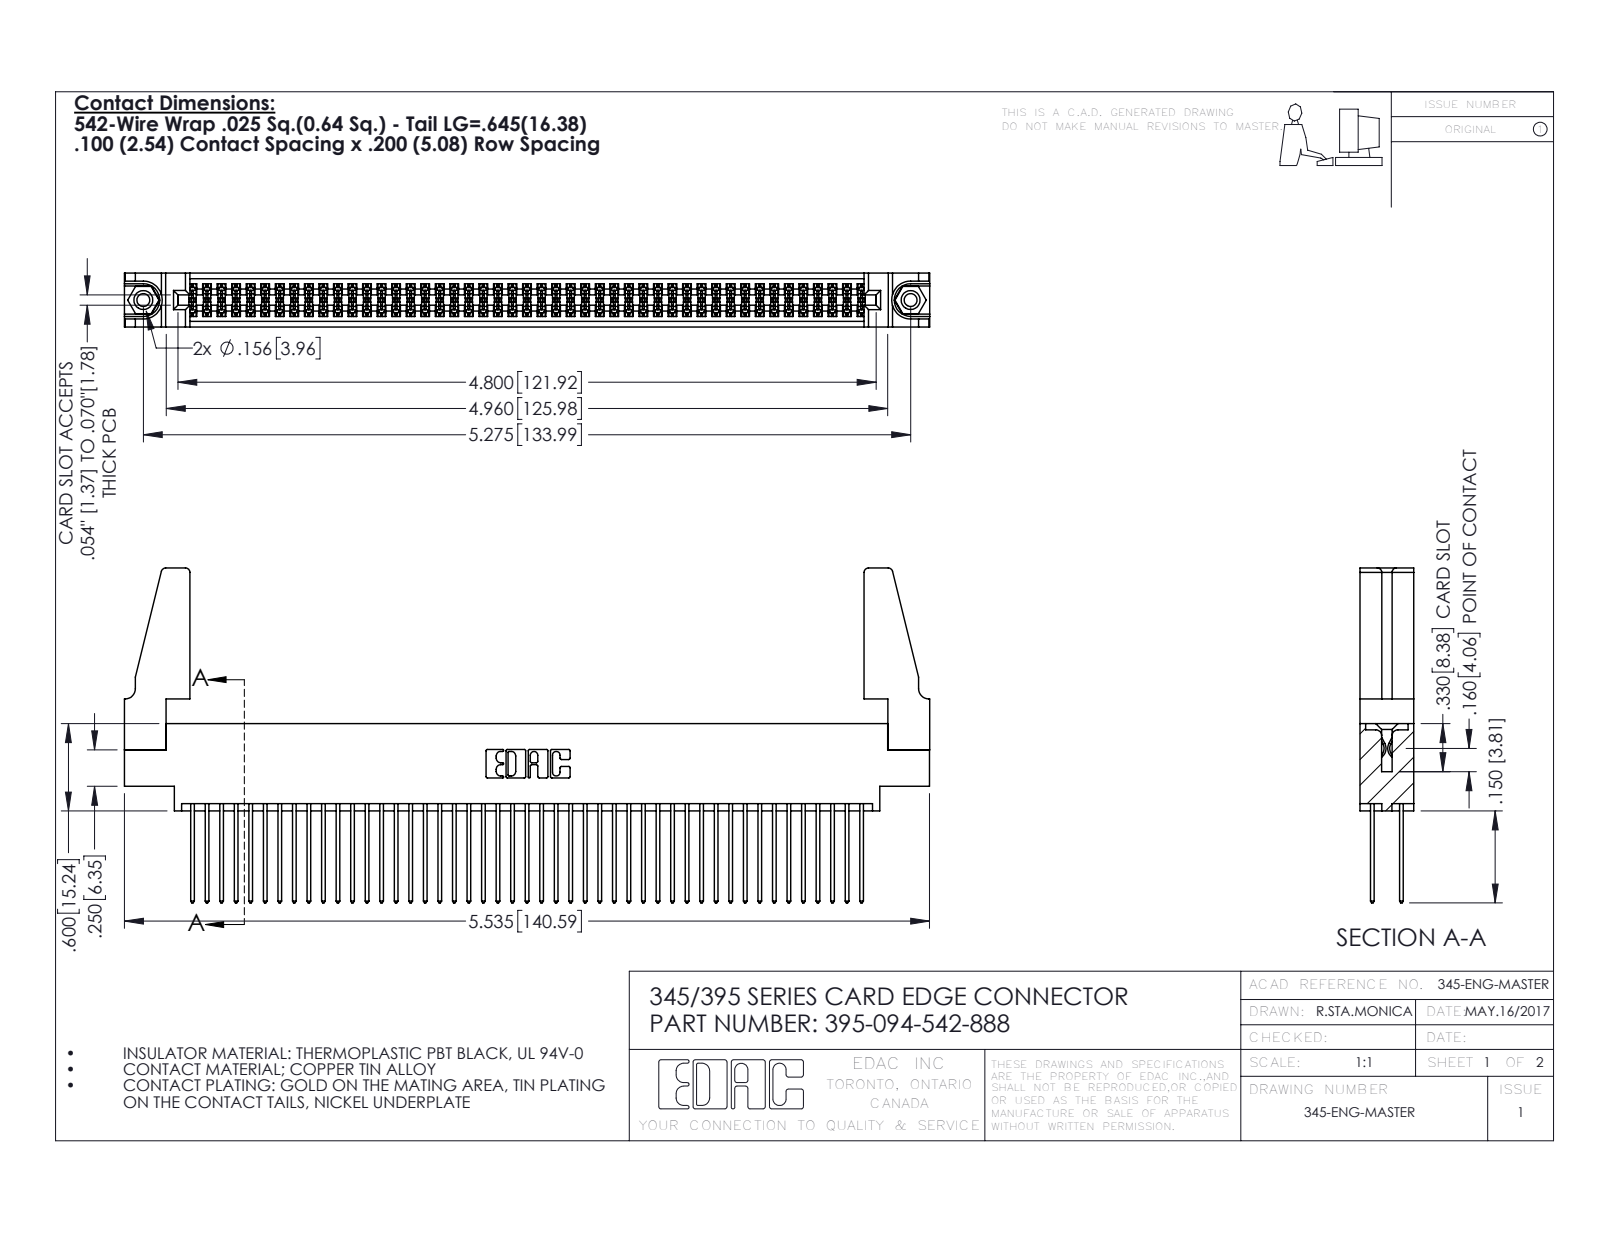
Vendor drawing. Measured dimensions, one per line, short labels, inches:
name: 345-250-001_345-250-001-102; 345 Part_0.170 Offset - 0.156 Dia-TH; 395-094-542-888; 345-220-078_345-220-088 (+1 more)
written by: SolidWorks 2016 (CONFIG_CONTROL_DESIGN)
unit: in
bodies: 99 solids, 4954 faces (3258 planar, 1680 cylindrical, 16 other)
size: 5.536 × 2.302 × 0.37
volume: 1.055 in³; area: 40.53 in²
holes: 2× ⌀0.089, 2× ⌀0.125, 2× ⌀0.156, 1× ⌀0.064
bosses: 2× ⌀0.155
rounds: 141× R0.006, 94× R0.01, 22× R0.01, 8× R0.03, 6× R0.007, 6× R0.031, 3× R0.026, 2× R0.014
face distances: 0.072, 0.298, 0.098, 0.272, 0.025, 0.2, 0.37, 0.225, 0.175, 0.149
hole spacings: 0.27, 5.039, 5.275
